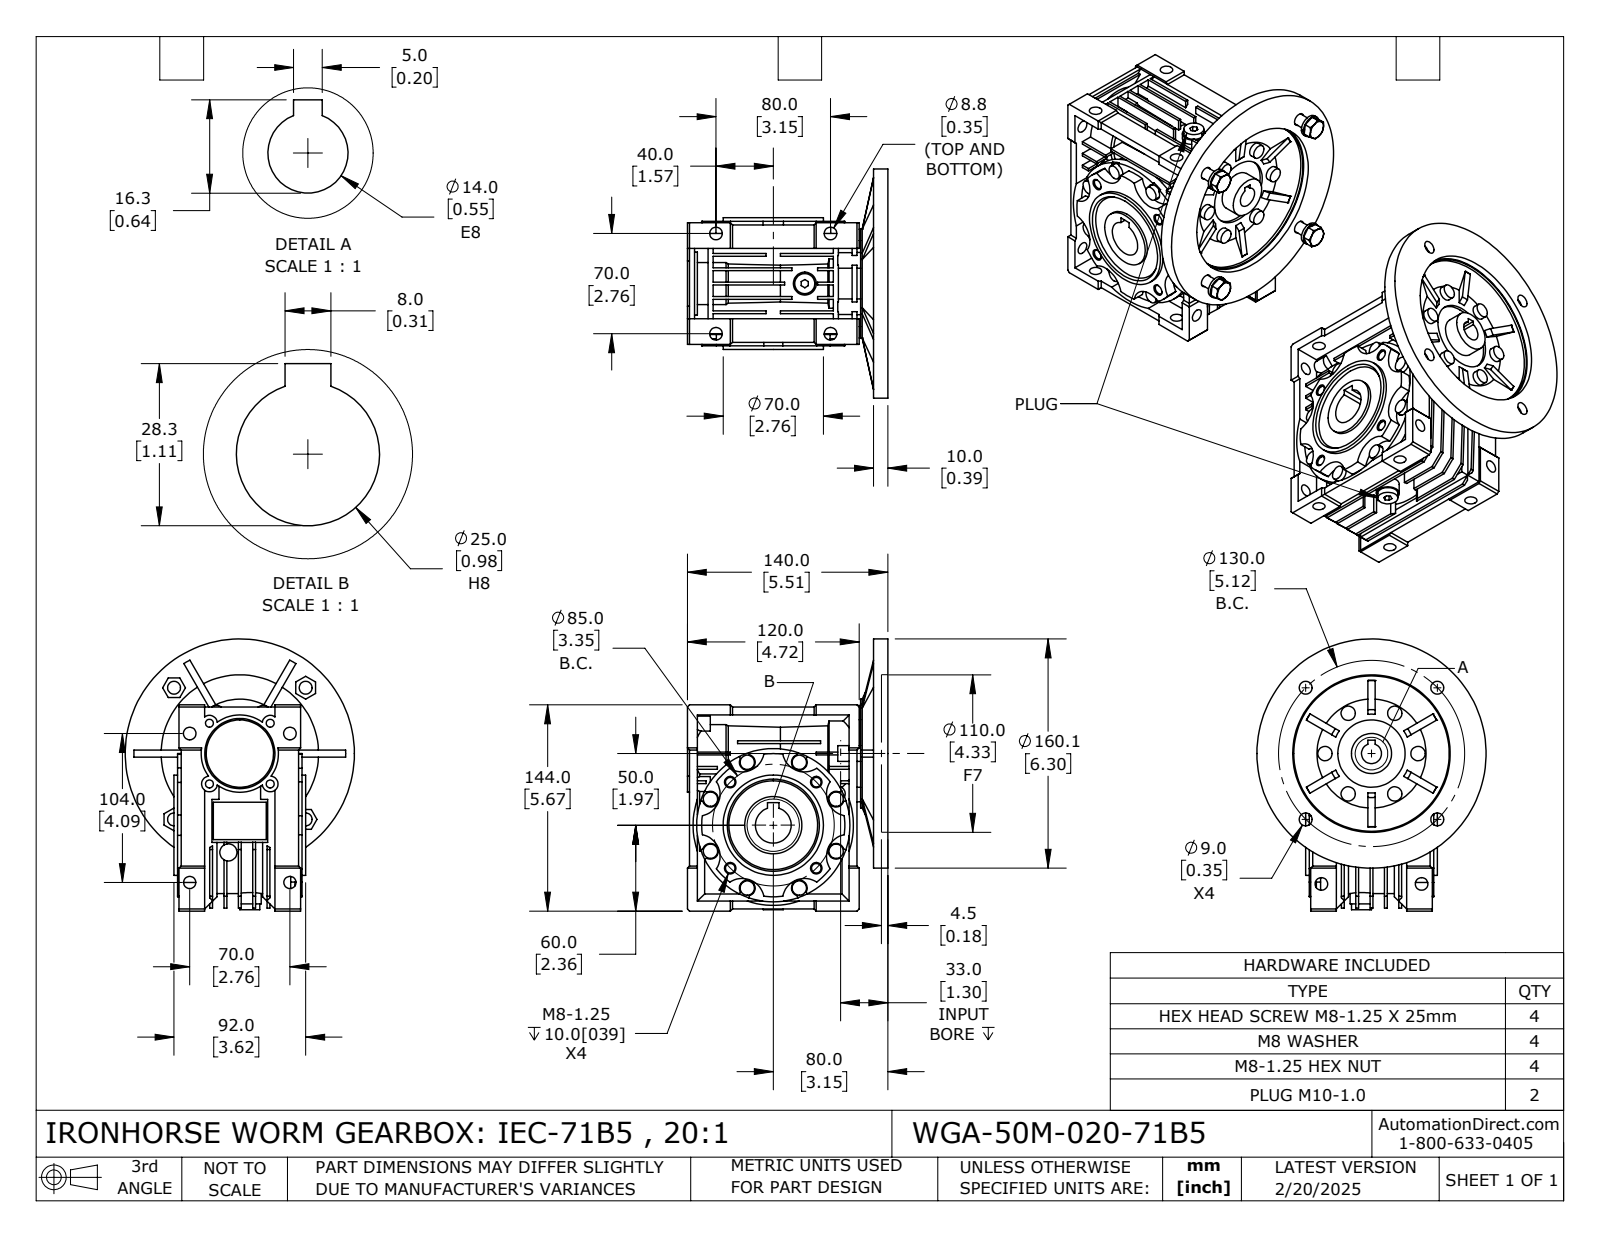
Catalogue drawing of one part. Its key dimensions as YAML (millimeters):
part_name: "WGA-50M-020-71B5"
step_written_by: "SolidWorks 2024 (CONFIG_CONTROL_DESIGN)"
units: millimeters
bodies: {solids: 7, faces: 1007, planar: 577, cylindrical: 316, other: 114}
overall_size: [190.03, 160.06, 140]
volume: 1146000
surface_area: 256628
round_holes:
  - {diameter: 8.8, count: 8}
  - {diameter: 8.5, count: 6}
  - {diameter: 9, count: 6}
  - {diameter: 5.55, count: 4}
  - {diameter: 6.65, count: 2}
  - {diameter: 6.65, count: 2}
  - {diameter: 14, count: 1}
  - {diameter: 15, count: 1}
  - {diameter: 25, count: 1}
  - {diameter: 28, count: 1}
  - {diameter: 34, count: 1}
  - {diameter: 40, count: 1}
round_bosses_or_shafts:
  - {diameter: 10, count: 14}
  - {diameter: 16, count: 2}
  - {diameter: 14, count: 2}
  - {diameter: 9.8, count: 2}
  - {diameter: 8.3, count: 2}
  - {diameter: 160.06, count: 1}
  - {diameter: 107, count: 1}
  - {diameter: 76, count: 1}
partial_cylinders:
  - {radius: 5.5, count: 18}
  - {radius: 6, count: 8}
  - {radius: 15, count: 8}
  - {radius: 15.5, count: 8}
  - {radius: 20.76, count: 1}
  - {radius: 46, count: 1}
  - {radius: 47.7, count: 1}
  - {radius: 50, count: 1}
face_to_face_distances: [10, 2, 7, 5.5, 8, 1.5, 20, 5, 55, 35]
hole_center_spacings: [71.58, 70, 30, 35, 42.42, 42.5, 60.1, 65]
